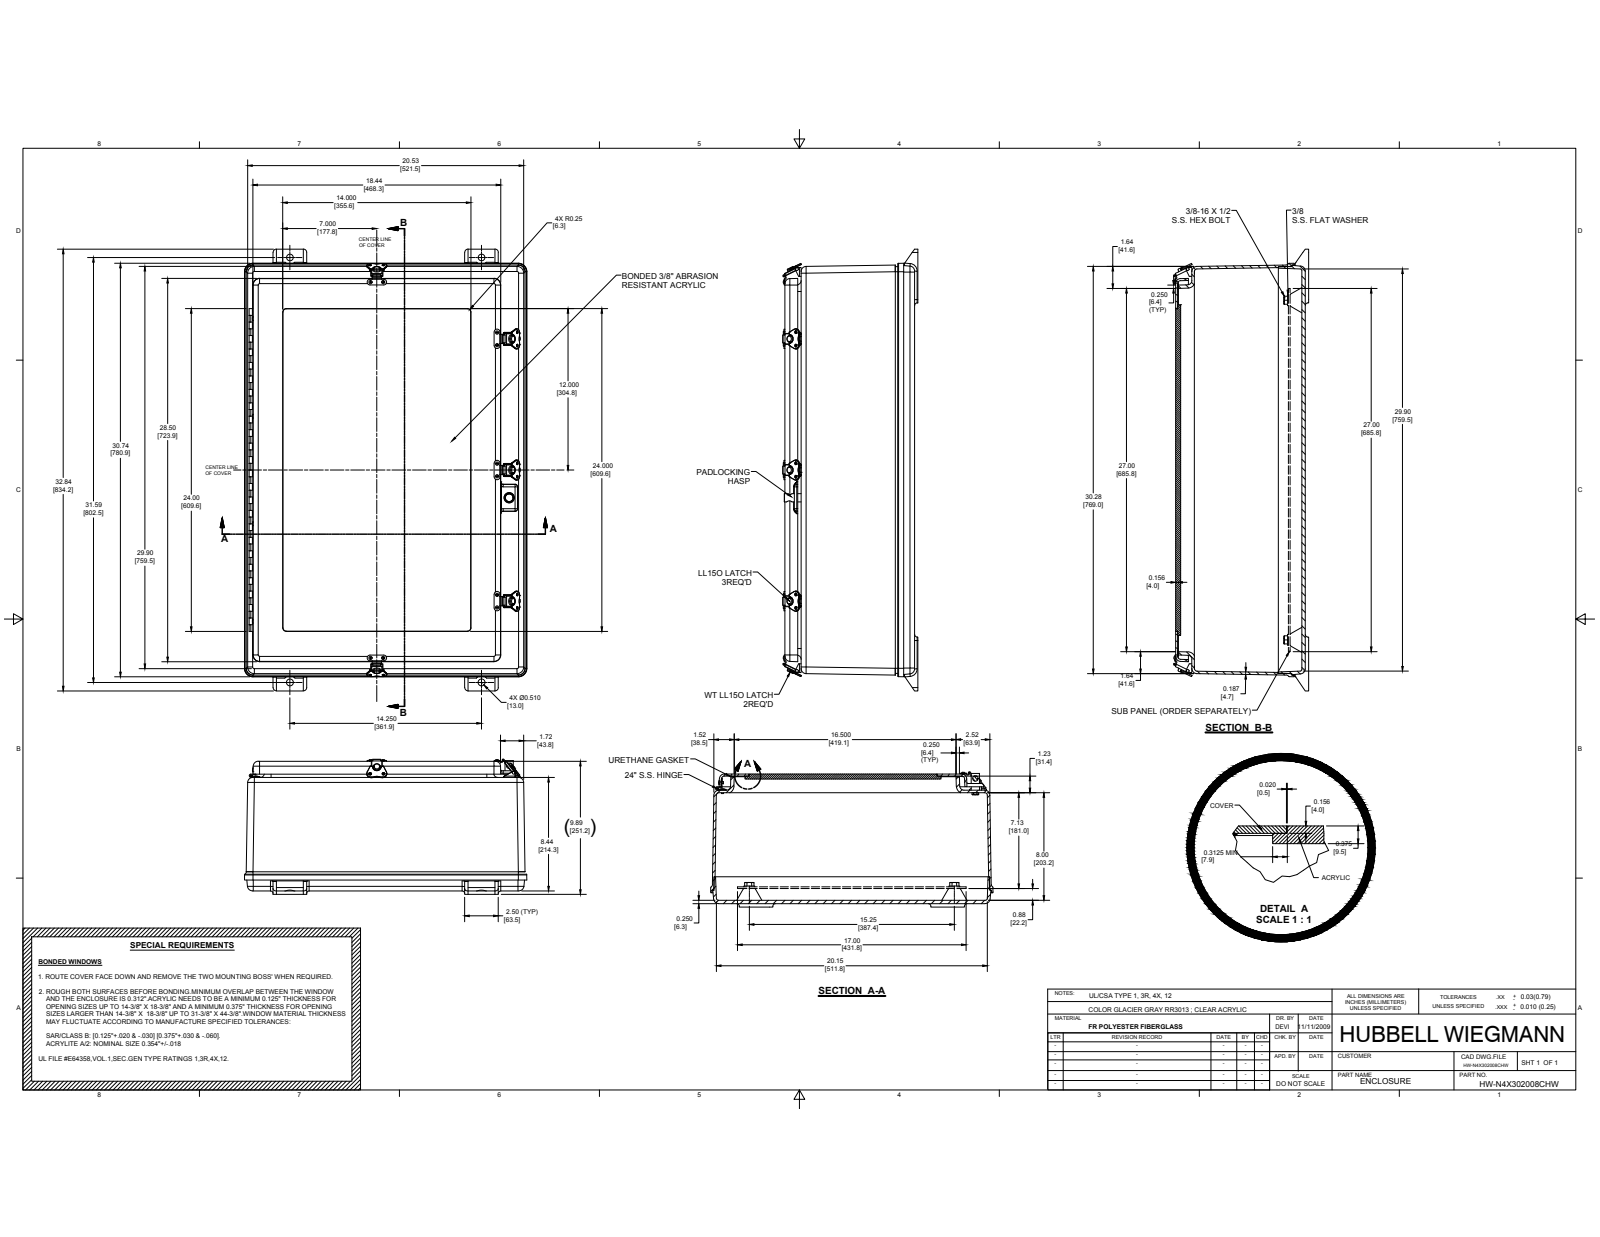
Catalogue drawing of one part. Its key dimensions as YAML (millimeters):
part_name: "WPN3020B; WPN30208SHWT; SS HINGE COVER (24); SS HINGE PIN (24) (+7 more)"
step_written_by: "Autodesk Inventor 2014 (AUTOMOTIVE_DESIGN)"
units: millimeters
bodies: {solids: 68, faces: 1857, planar: 713, cylindrical: 722, other: 422}
overall_size: [834.23, 533.4, 255.41]
volume: 9184000
surface_area: 3361000
round_holes:
  - {diameter: 3.3, count: 36}
  - {diameter: 1.59, count: 20}
  - {diameter: 3.5, count: 10}
  - {diameter: 4.76, count: 10}
  - {diameter: 1.65, count: 8}
  - {diameter: 7.8, count: 4}
  - {diameter: 14.3, count: 4}
  - {diameter: 3.43, count: 3}
  - {diameter: 3.97, count: 3}
  - {diameter: 12.7, count: 2}
  - {diameter: 12.96, count: 2}
  - {diameter: 3.17, count: 1}
round_bosses_or_shafts:
  - {diameter: 3.56, count: 20}
  - {diameter: 7.54, count: 8}
  - {diameter: 12.7, count: 5}
  - {diameter: 5.08, count: 3}
  - {diameter: 6.35, count: 1}
  - {diameter: 5.11, count: 1}
partial_cylinders:
  - {radius: 0.25, count: 127}
  - {radius: 6.35, count: 28}
  - {radius: 4.76, count: 21}
  - {radius: 0.76, count: 20}
  - {radius: 7.94, count: 19}
  - {radius: 9.53, count: 17}
  - {radius: 12.7, count: 12}
  - {radius: 1.59, count: 10}
face_to_face_distances: [6.35, 4.76, 244.94, 238.59, 235.42, 229.07, 9.52, 3.96, 240.98, 234.63]
hole_center_spacings: [247.65, 184.15, 387.35, 25.4, 81.56, 248.38, 383.21, 495.3]
